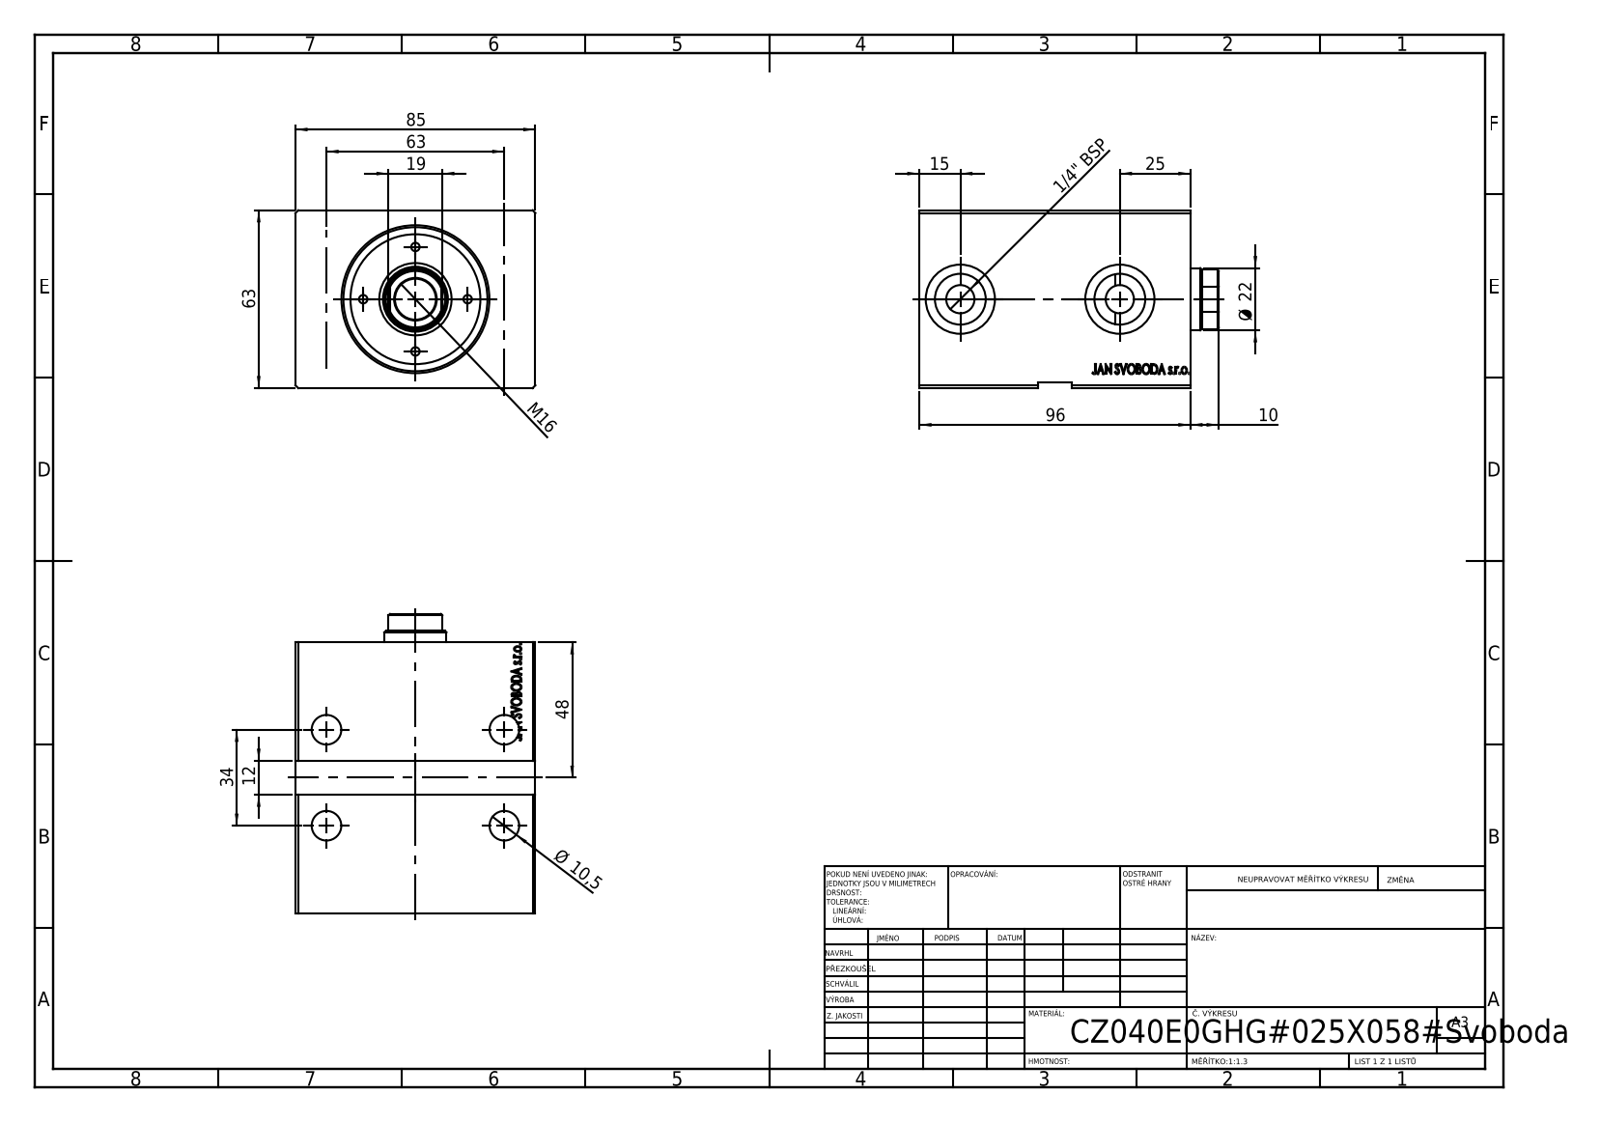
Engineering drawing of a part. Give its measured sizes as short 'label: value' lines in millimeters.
written by: SolidWorks 2019 (CONFIG_CONTROL_DESIGN)
unit: mm
bodies: 1 solid, 797 faces (383 planar, 30 cylindrical, 384 other)
size: 96 × 85 × 63
volume: 373 045 mm³; area: 58 921 mm²
holes: 4× ⌀10.5, 2× ⌀8, 2× ⌀10, 2× ⌀18, 2× ⌀24.5, 1× ⌀36, 1× ⌀40, 1× ⌀51
face distances: 63, 85, 96, 80.7, 15.3, 2, 61, 95.8, 15.1, 10
hole spacings: 34, 63, 71.59, 17.95, 18.67, 34.73, 36.5, 44.12
